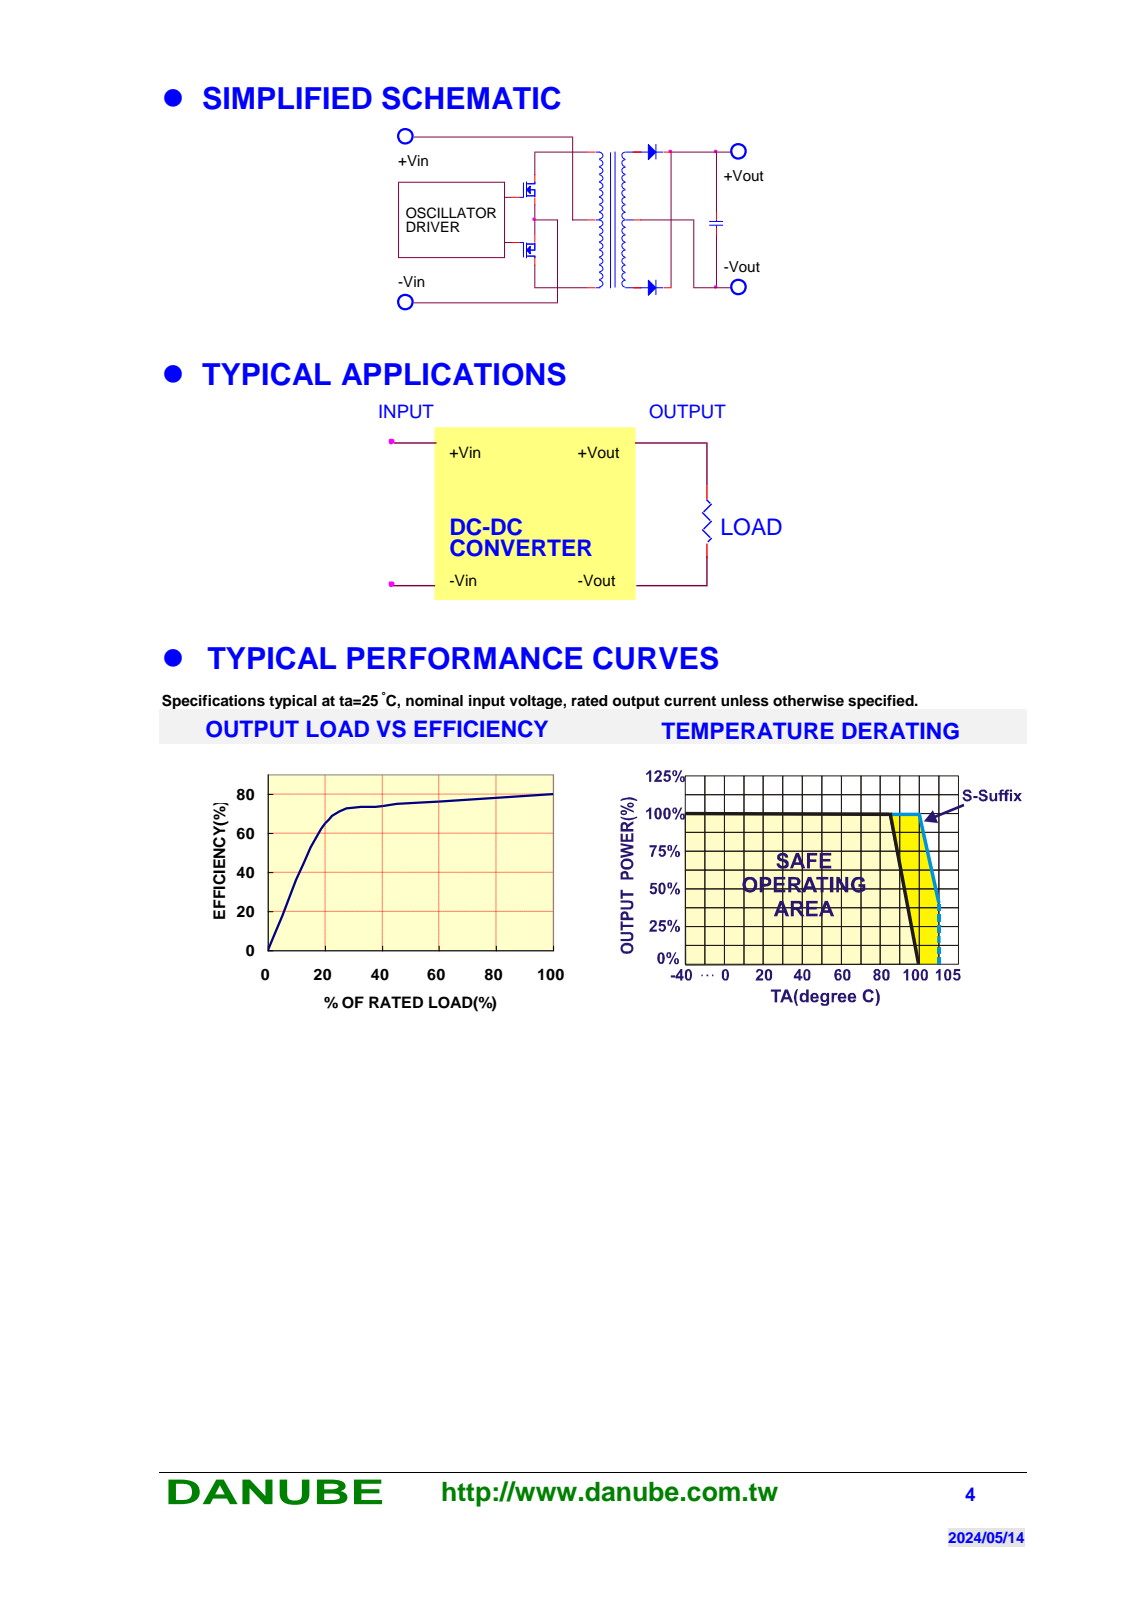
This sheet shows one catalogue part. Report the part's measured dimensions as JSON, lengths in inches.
{"part_name": "case; pin_2; pin_4; pin_8 (+2 more)", "step_written_by": "FreeCAD (AUTOMOTIVE_DESIGN)", "units": "inches", "bodies": {"solids": 6, "faces": 84, "planar": 80, "cylindrical": 4, "other": 0}, "overall_size": [0.508, 0.437, 0.283], "volume_in3": 0.054, "surface_area_in2": 0.924, "partial_cylinders_radius": [[0.035, 4]], "face_to_face_distances": [0.272, 0.508, 0.016, 0.256, 0.02, 0.346, 0.094, 0.114, 0.394, 0.414]}
